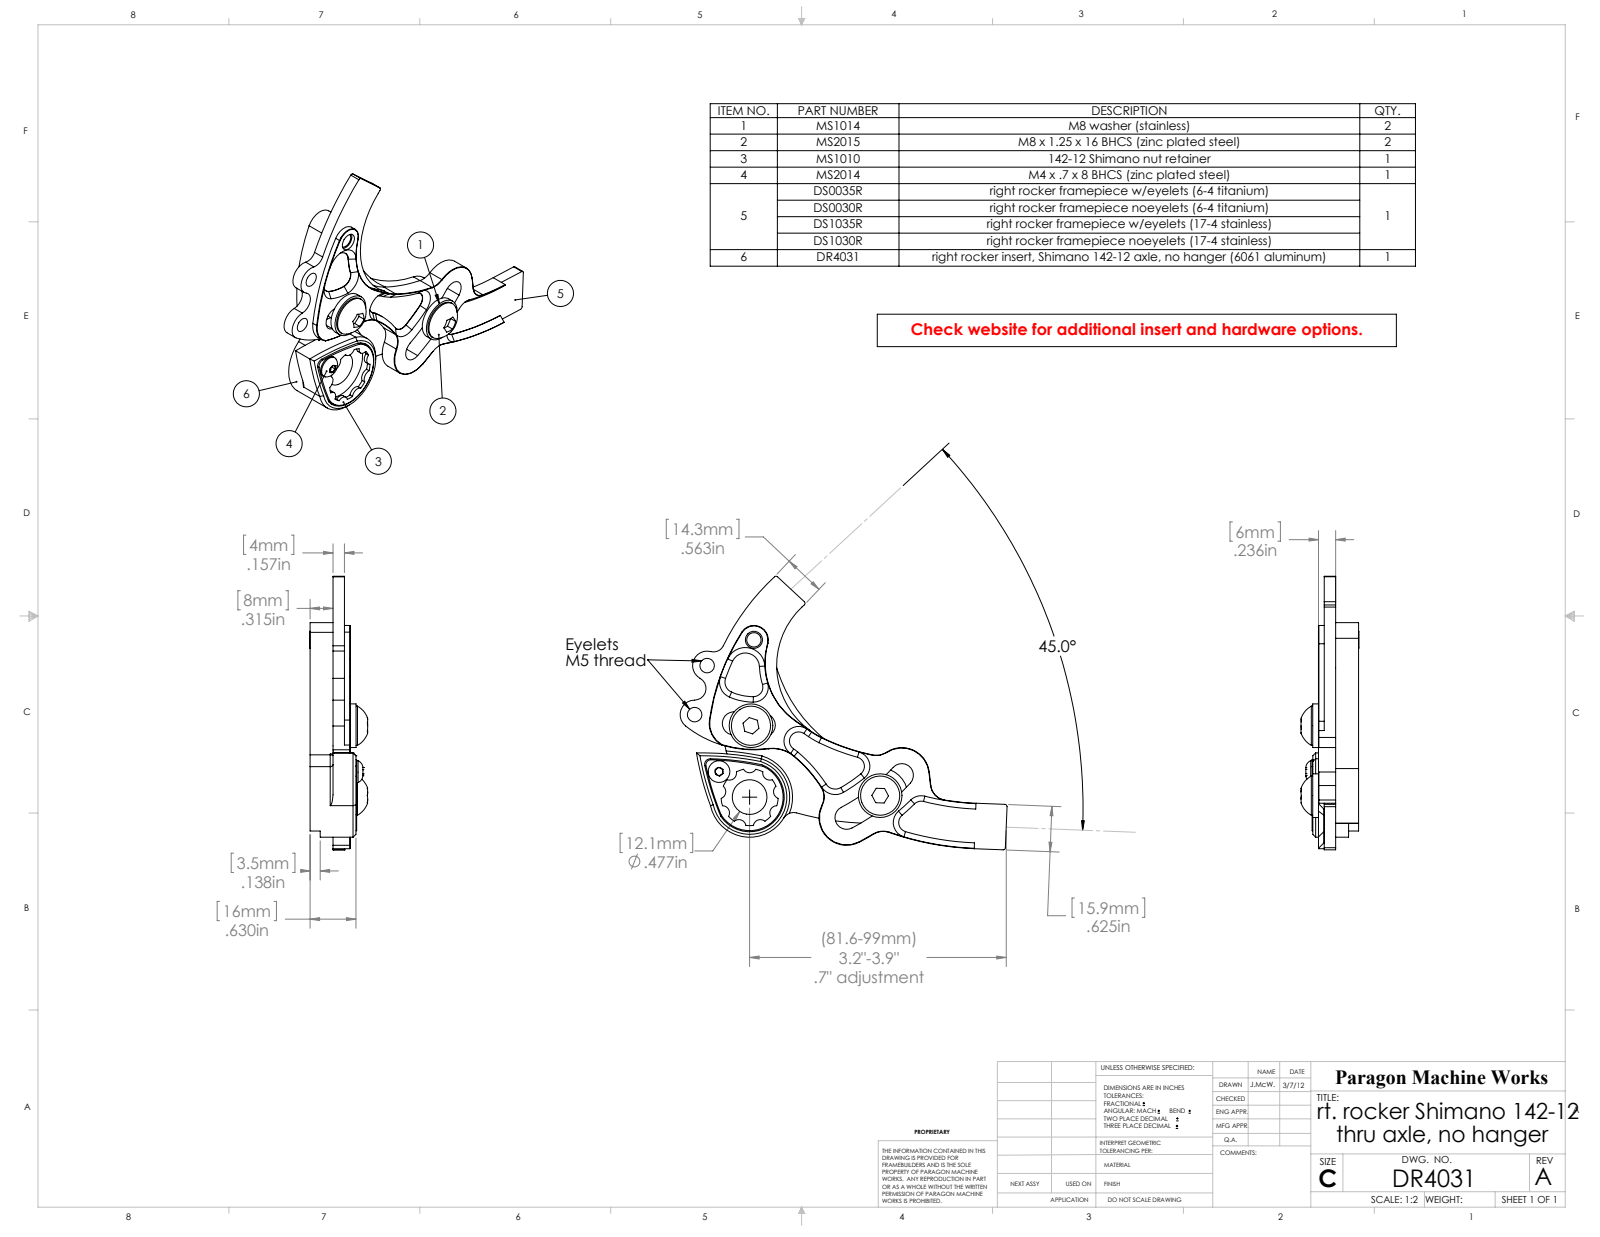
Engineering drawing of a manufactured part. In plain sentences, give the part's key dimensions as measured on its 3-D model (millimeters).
The part is named "DR4031; DS0035R; MS2014_92095A189; MS1010 (+3 more)". Its 3-D file was written by "SolidWorks 2012 (AUTOMOTIVE_DESIGN)". It is 9 solids with 253 faces: 65 planar, 127 cylindrical and 61 other. Overall it measures 114.2 by 95.5 by 20.2 millimeters. Its volume is 34 120 cubic millimeters and its surface area 21 920 square millimeters. Round holes: 2 of diameter 5.1, 2 of diameter 8.3, 1 of diameter 3.3, 1 of diameter 4.2, 1 of diameter 6, 1 of diameter 8, 1 of diameter 8, 1 of diameter 12.1, 1 of diameter 22. Round bosses or shafts: 2 of diameter 15.2, 2 of diameter 13.7, 1 of diameter 28, 1 of diameter 8, 1 of diameter 7.6, 1 of diameter 6.4, 1 of diameter 4, 1 of diameter 3.1. Partial cylindrical surfaces (rounded edges, fillets, slot ends): 9 of radius 2.5, 5 of radius 3.8, 5 of radius 4.1, 4 of radius 0.8, 4 of radius 3.3, 3 of radius 6.4, 3 of radius 9.7, 2 of radius 0.1. The main face-to-face distances are 3.5, 8, 4, 4.5, 12, 6, 14, 2, 7.5, 9.5. The hole center spacings are 13.9, 17.7, 18.6, 19.5, 20.1, 21.6, 24.9, 26.
